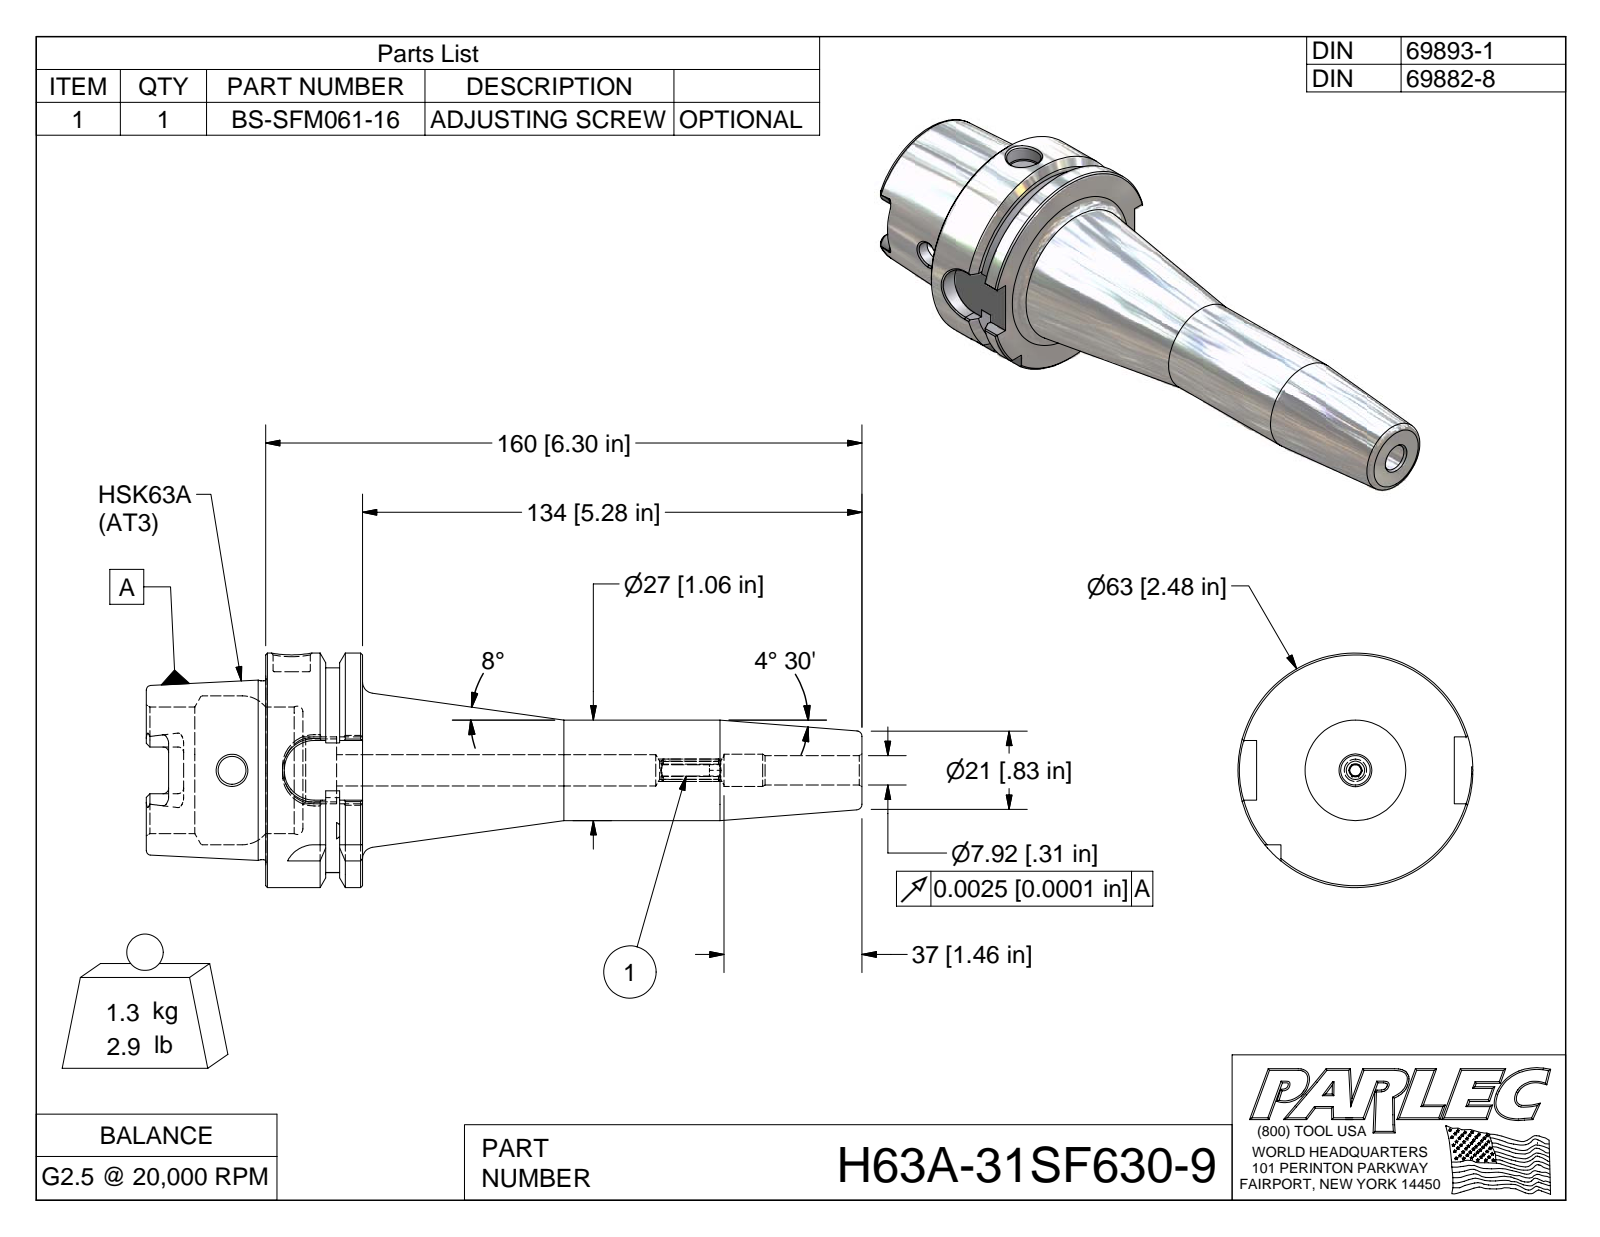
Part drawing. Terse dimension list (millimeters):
name: H63A-31SF630-9; H63A-31SF630-9-1; BS-SFM061-16
written by: Autodesk Inventor 2009 (AUTOMOTIVE_DESIGN)
unit: mm
bodies: 2 solids, 165 faces (59 planar, 35 cylindrical, 71 other)
size: 192 × 63 × 63
volume: 168 300 mm³; area: 37 290 mm²
holes: 1× ⌀7.5, 1× ⌀7.9, 1× ⌀8.7, 1× ⌀10, 1× ⌀16.9, 1× ⌀34, 1× ⌀40
bosses: 1× ⌀63, 1× ⌀48, 1× ⌀27
rounds: 6× R1.5, 4× R2.9, 4× R8, 1× R3, 1× R27.5
face distances: 26, 6.1, 9.9, 10, 16, 32, 42, 58, 48.1, 16.1
